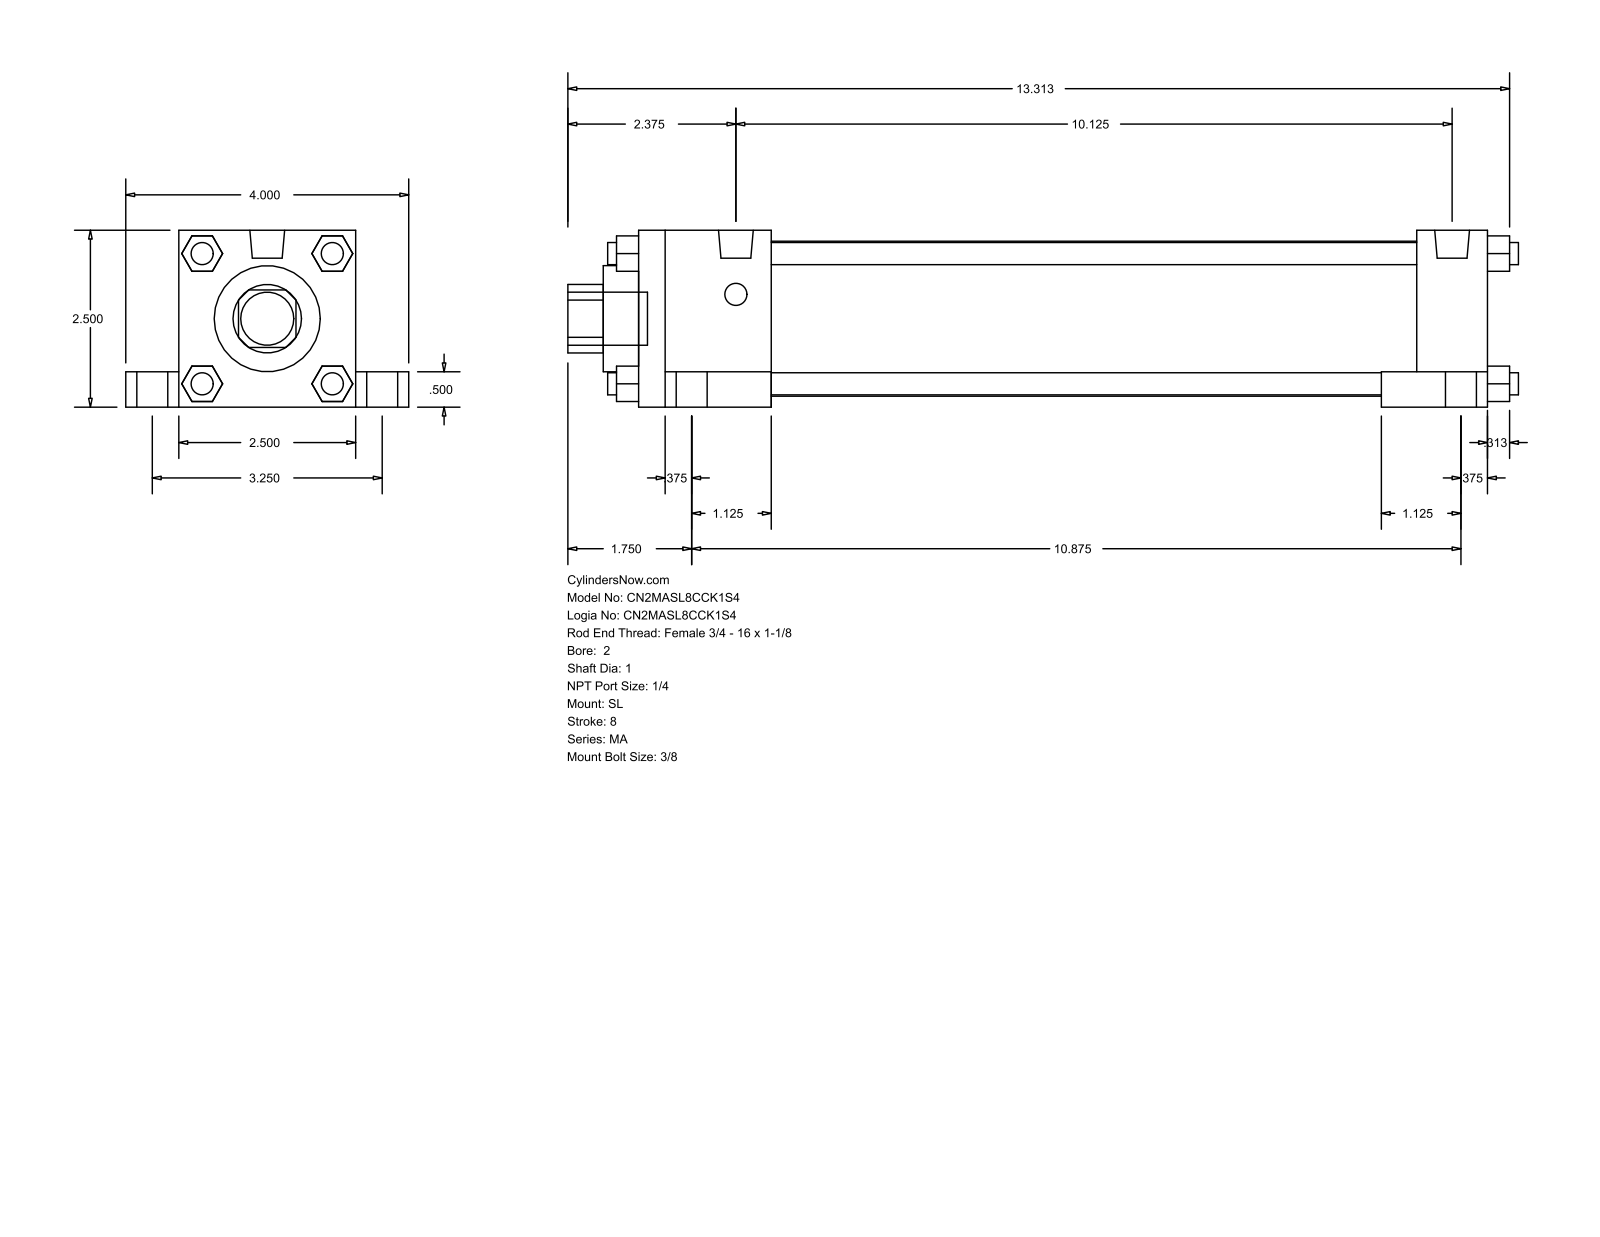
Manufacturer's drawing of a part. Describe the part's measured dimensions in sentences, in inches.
The part is named "MA_SL__0200_1". Its 3-D file was written by "GSSL Pune (CONFIG_CONTROL_DESIGN)". It is 0 solids with 148 faces: 112 planar, 36 cylindrical and 0 other. Overall it measures 13.437 by 4 by 2.5 inches. Round holes: 1 of diameter 1, 1 of diameter 1.5, 1 of diameter 2.19. Round bosses or shafts: 8 of diameter 0.313, 4 of diameter 0.687, 4 of diameter 0.437, 2 of diameter 0.492, 1 of diameter 0.75. Partial cylindrical surfaces (rounded edges, fillets, slot ends): 1 of radius 0.484. The main face-to-face distances are 2.5, 0.5, 12, 0.75, 3.25, 1, 2, 1.875, 10.125, 11.
